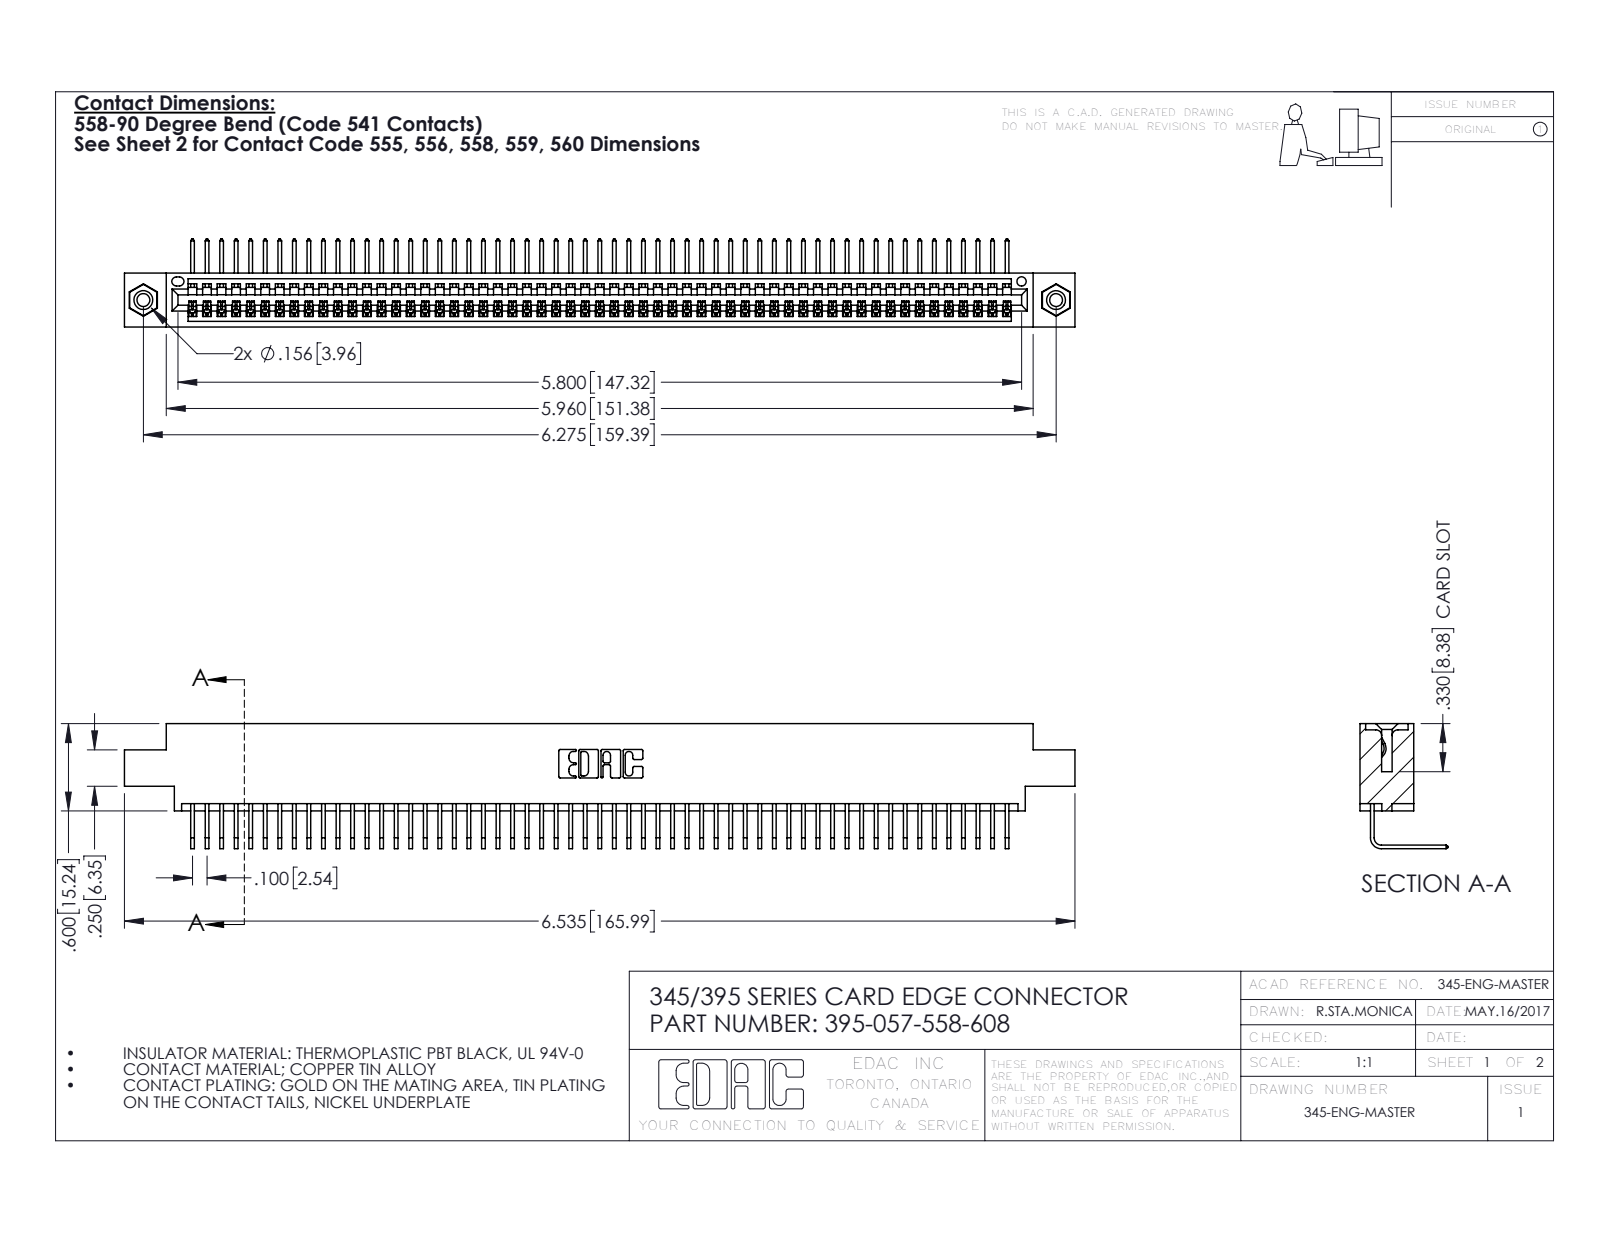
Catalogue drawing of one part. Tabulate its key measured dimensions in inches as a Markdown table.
| quantity | value |
| --- | --- |
| part name | 345-292-001_558 Tail - 2; 345-250-001_345-250-003-102; 345 Part_0.170 Offset - 0.156 Dia-TI; 395-057-558-608 |
| STEP written by | SolidWorks 2016 (CONFIG_CONTROL_DESIGN) |
| units | inches |
| bodies | 60 solids, 3610 faces (2510 planar, 1084 cylindrical, 16 other) |
| overall size | 6.535 × 0.859 × 0.605 |
| volume | 0.974 in³ |
| surface area | 35.14 in² |
| round holes (diameter × count) | 0.089 × 2, 0.125 × 2, 0.156 × 2, 0.064 × 1 |
| round bosses / shafts (diameter × count) | 0.155 × 2 |
| partial cylindrical surfaces (radius × count) | 0.006 × 114, 0.01 × 22, 0.007 × 6, 0.031 × 6, 0.026 × 3, 0.031 × 2, 0.04 × 2, 0.014 × 1 |
| main face-to-face distances | 0.072, 0.298, 0.37, 0.2, 0.098, 0.272, 0.025, 0.225, 0.175, 0.149 |
| hole center spacings | 0.27, 6.039, 6.275 |
